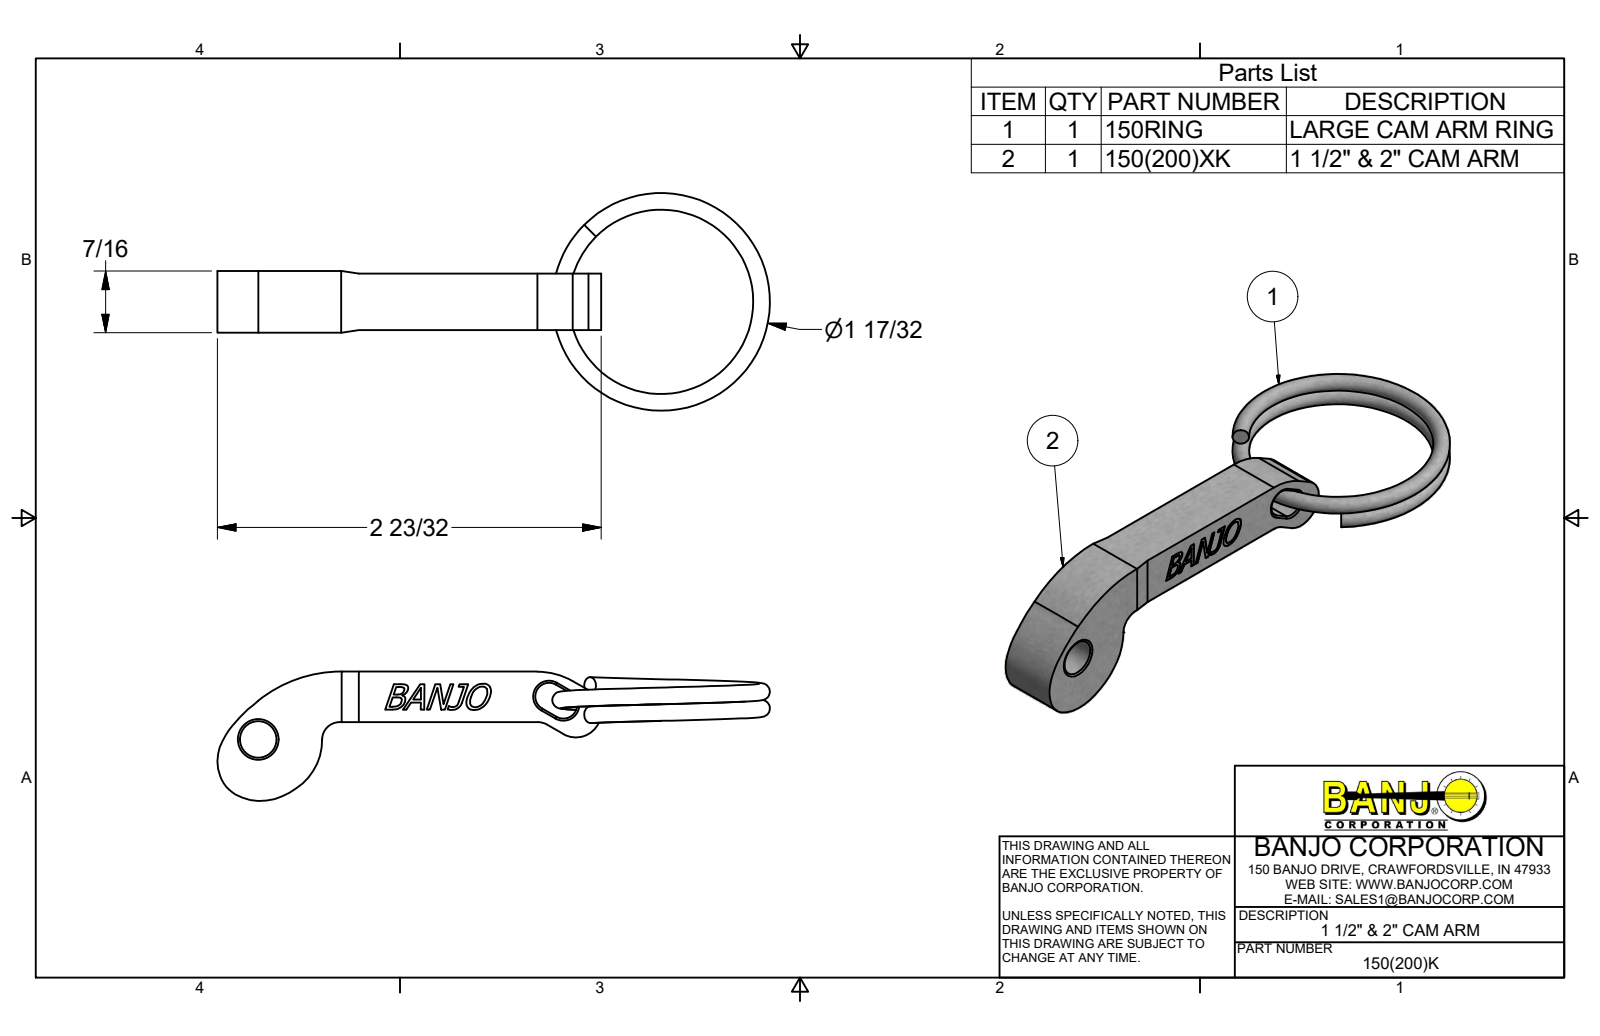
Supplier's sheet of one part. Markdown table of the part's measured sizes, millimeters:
| quantity | value |
| --- | --- |
| part name | 150(200)K; 150(200)XK; 150RING |
| STEP written by | Autodesk Inventor 2017 (AUTOMOTIVE_DESIGN) |
| units | millimeters |
| bodies | 2 solids, 192 faces (109 planar, 8 cylindrical, 75 other) |
| overall size | 99.39 × 39.14 × 23.25 |
| volume | 8 784 mm³ |
| surface area | 5 452 mm² |
| round holes (diameter × count) | 6.55 × 1 |
| partial cylindrical surfaces (radius × count) | 2.48 × 2, 3.15 × 1, 3.17 × 1, 4.55 × 1, 12.7 × 1, 23.88 × 1 |
| main face-to-face distances | 0.48, 10.64, 9.09, 10.16, 11.12, 0.51, 10.61, 10.13, 2.07, 7.03 |
